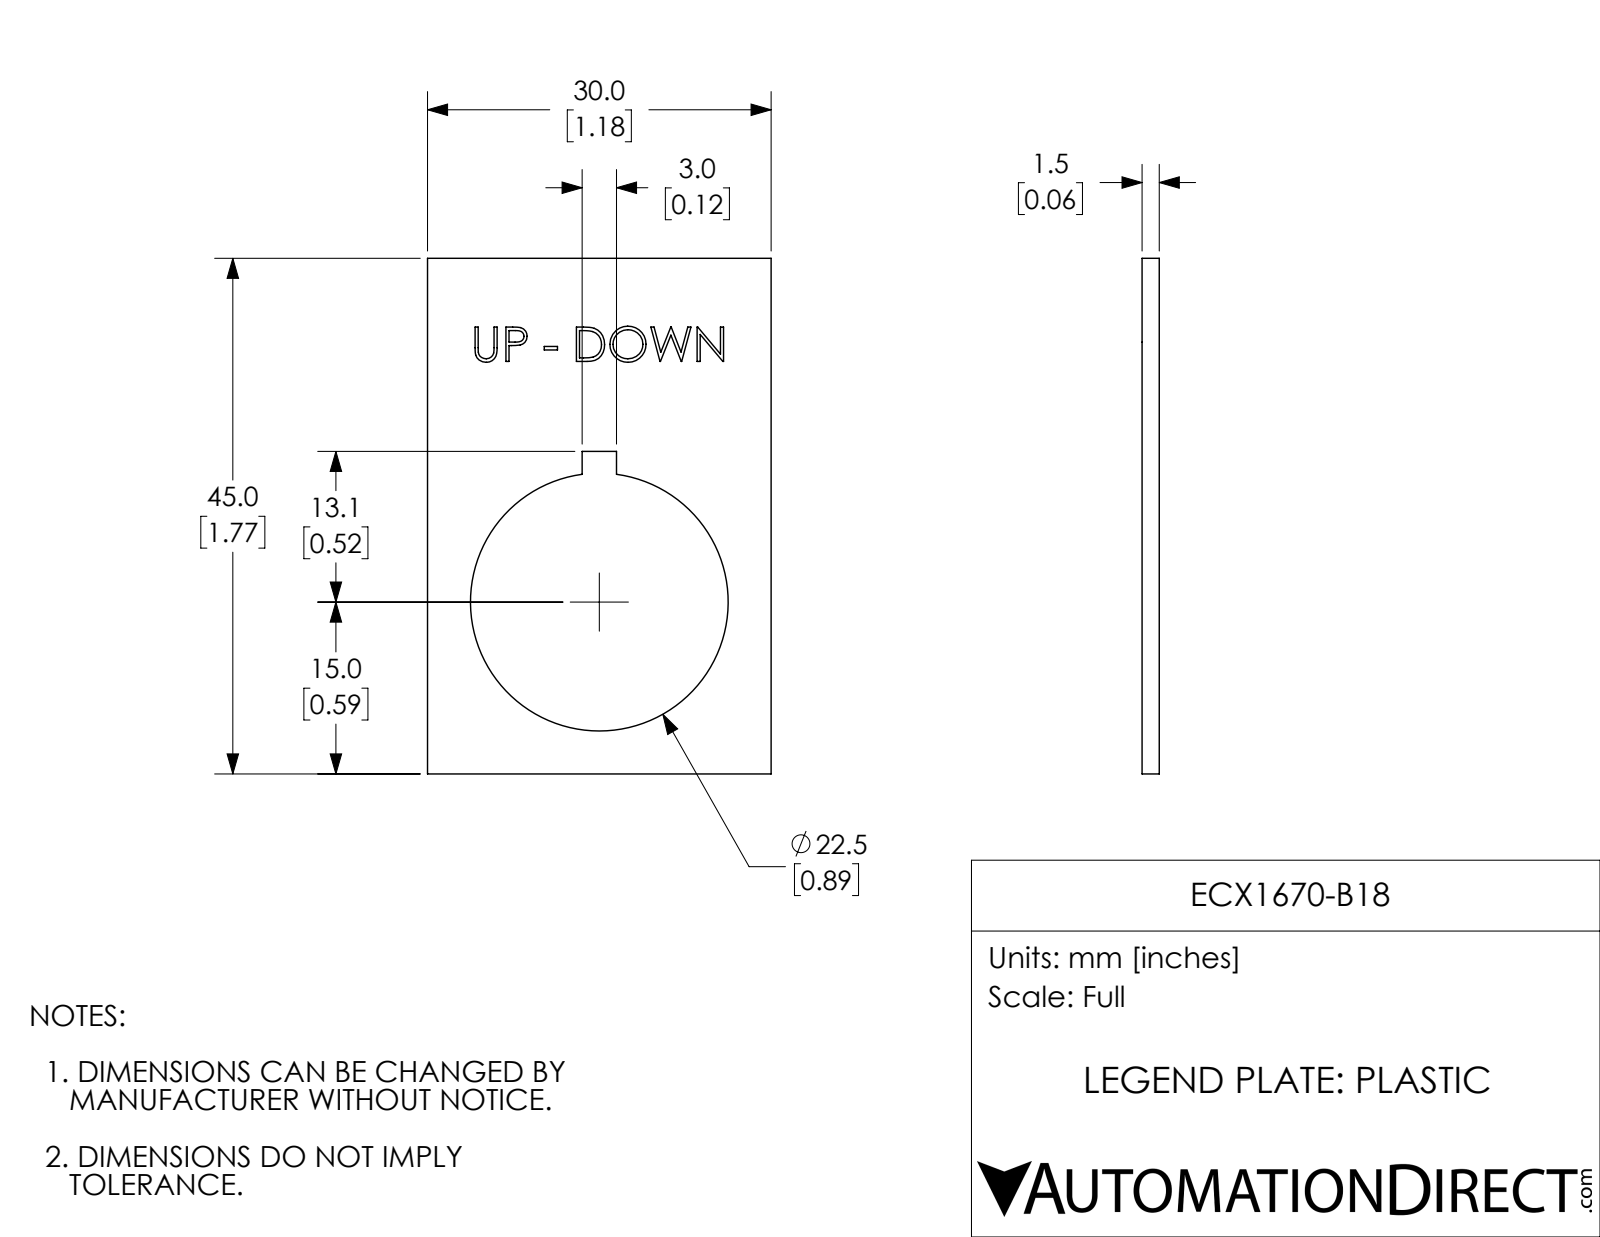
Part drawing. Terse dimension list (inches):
name: ECX1670-B18
written by: SolidWorks 2017 (AUTOMOTIVE_DESIGN)
unit: in
bodies: 1 solid, 97 faces (66 planar, 3 cylindrical, 28 other)
size: 1.772 × 1.181 × 0.059
volume: 0.087 in³; area: 3.461 in²
holes: 1× ⌀0.886
face distances: 0.059, 1.181, 1.772, 0.058, 0.531, 0.65, 1.108, 0.663, 0.118, 0.415
